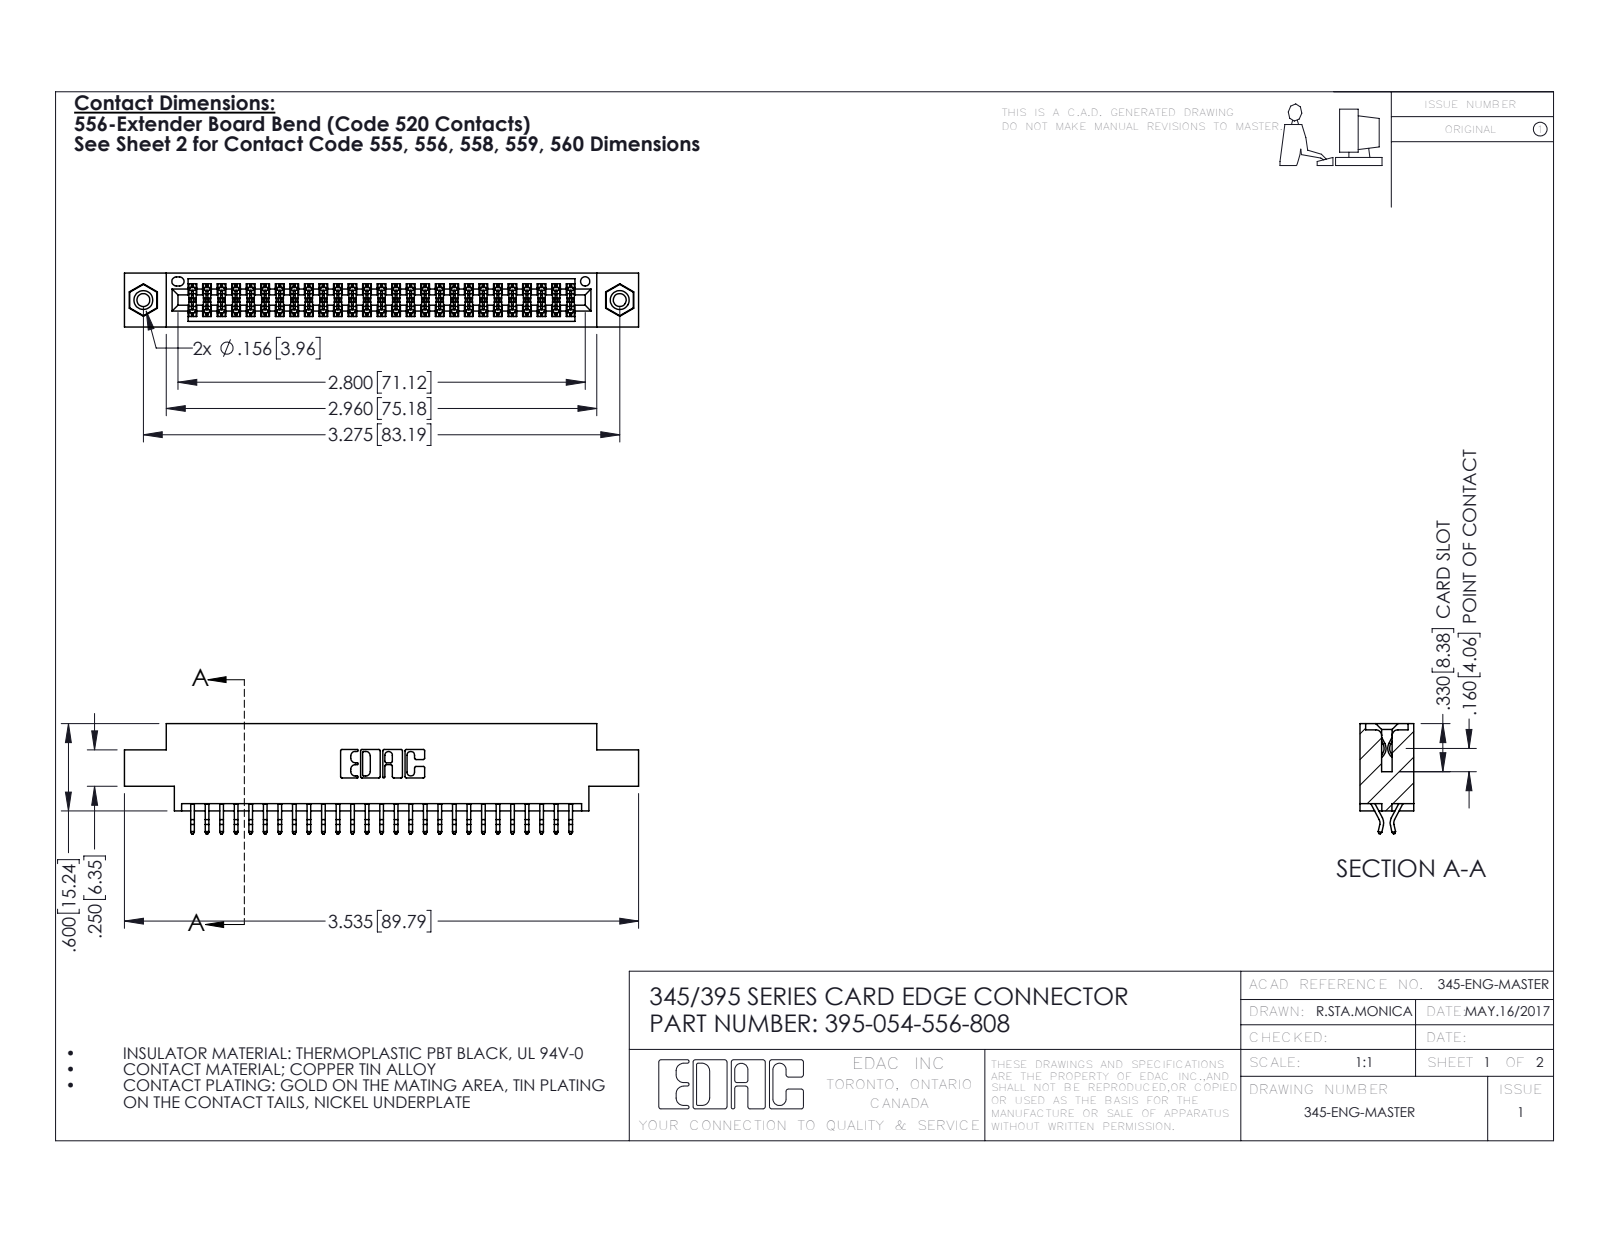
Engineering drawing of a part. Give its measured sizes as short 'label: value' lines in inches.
name: 345 Part_0.170 Offset - 0.156 Dia-TI; 345-292-001_556 Tail; 345-250-001_345-250-003-102; 395-054-556-808
written by: SolidWorks 2016 (CONFIG_CONTROL_DESIGN)
unit: in
bodies: 57 solids, 3214 faces (2114 planar, 1084 cylindrical, 16 other)
size: 3.535 × 0.757 × 0.37
volume: 0.516 in³; area: 19.1 in²
holes: 2× ⌀0.089, 2× ⌀0.125, 2× ⌀0.156, 1× ⌀0.064
bosses: 2× ⌀0.155
rounds: 81× R0.006, 22× R0.01, 6× R0.007, 6× R0.031, 3× R0.026, 2× R0.01, 2× R0.014, 2× R0.019
face distances: 0.072, 0.298, 0.37, 0.2, 0.025, 0.098, 0.272, 0.225, 0.175, 0.149
hole spacings: 0.27, 3.04, 3.275
